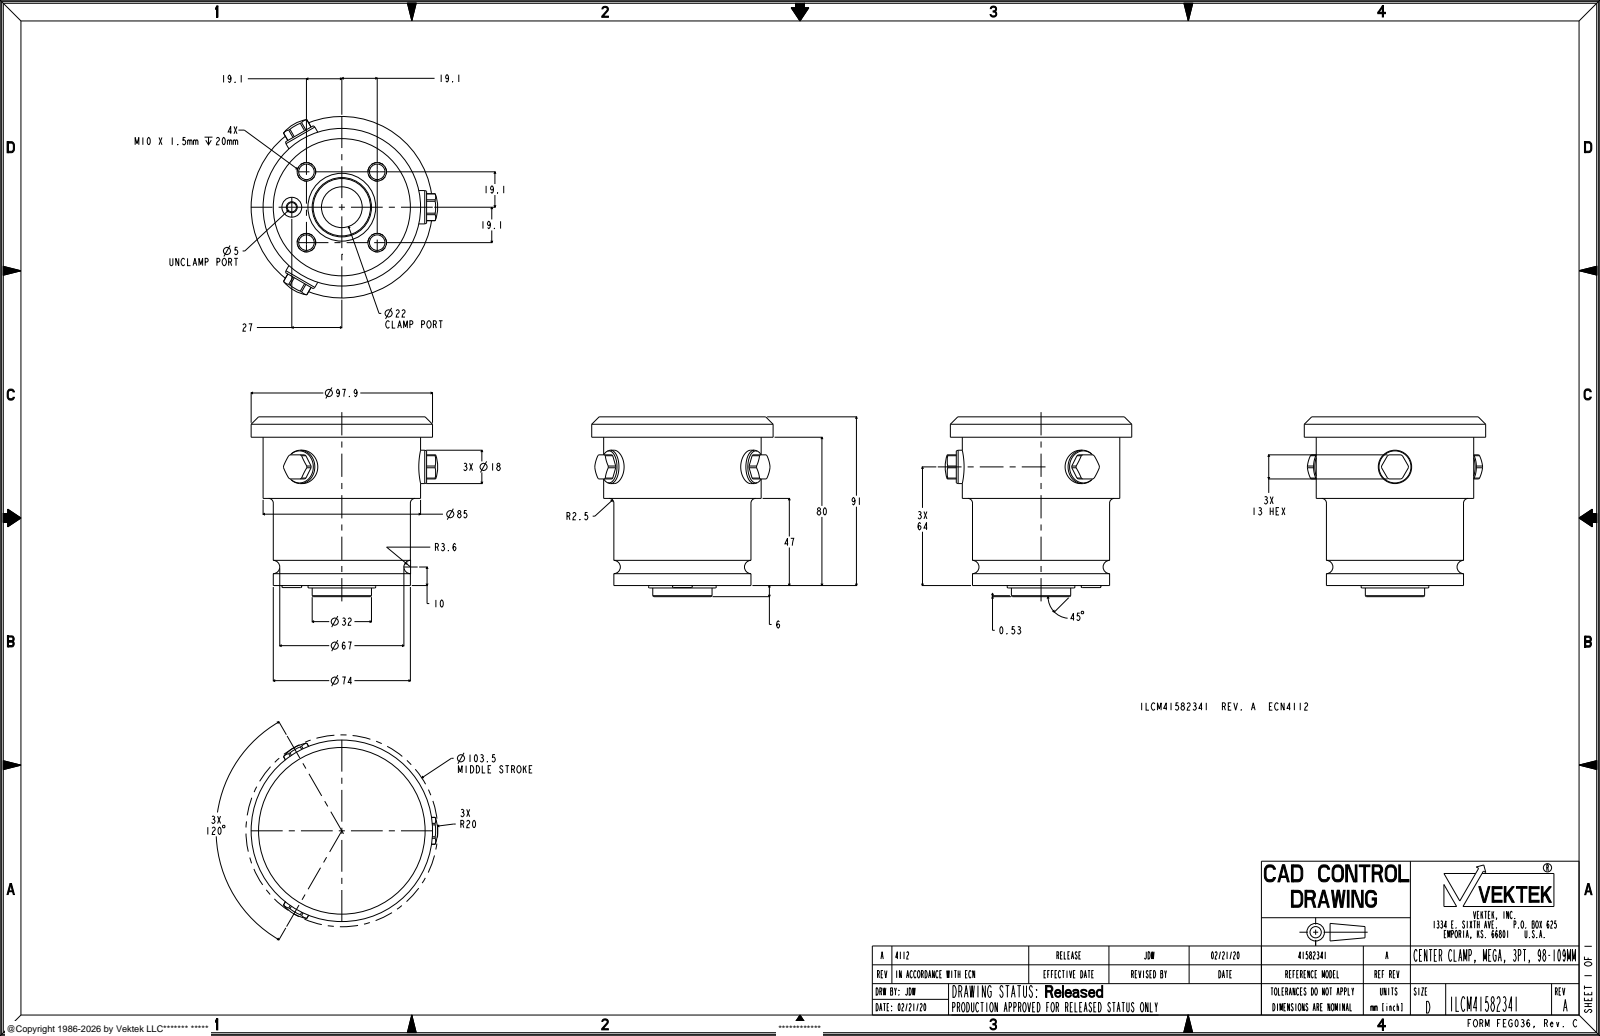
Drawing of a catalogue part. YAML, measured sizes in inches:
part_name: "ILCM41582341"
step_written_by: "PRO/ENGINEER BY PARAMETRIC TECHNOLOGY CORPORATION, 2013320 (AUTOMOTIVE_DESIGN)"
units: inches
bodies: {solids: 1, faces: 158, planar: 46, cylindrical: 64, other: 48}
overall_size: [3.965, 3.854, 3.819]
volume: 28.45
surface_area: 74.66
round_holes:
  - {diameter: 0.33, count: 4}
  - {diameter: 0.709, count: 3}
  - {diameter: 0.197, count: 1}
  - {diameter: 0.866, count: 1}
round_bosses_or_shafts:
  - {diameter: 0.394, count: 4}
  - {diameter: 3.854, count: 1}
  - {diameter: 3.346, count: 1}
  - {diameter: 2.913, count: 1}
  - {diameter: 1.441, count: 1}
  - {diameter: 1.26, count: 1}
partial_cylinders:
  - {radius: 0.285, count: 3}
face_to_face_distances: [3.583, 3.15, 0.433, 1.85, 1.299, 1.732, 0.148, 0.118, 1.969, 3.268]
hole_center_spacings: [1.063, 1.504, 0.814, 1.965, 2.127, 1.063]
